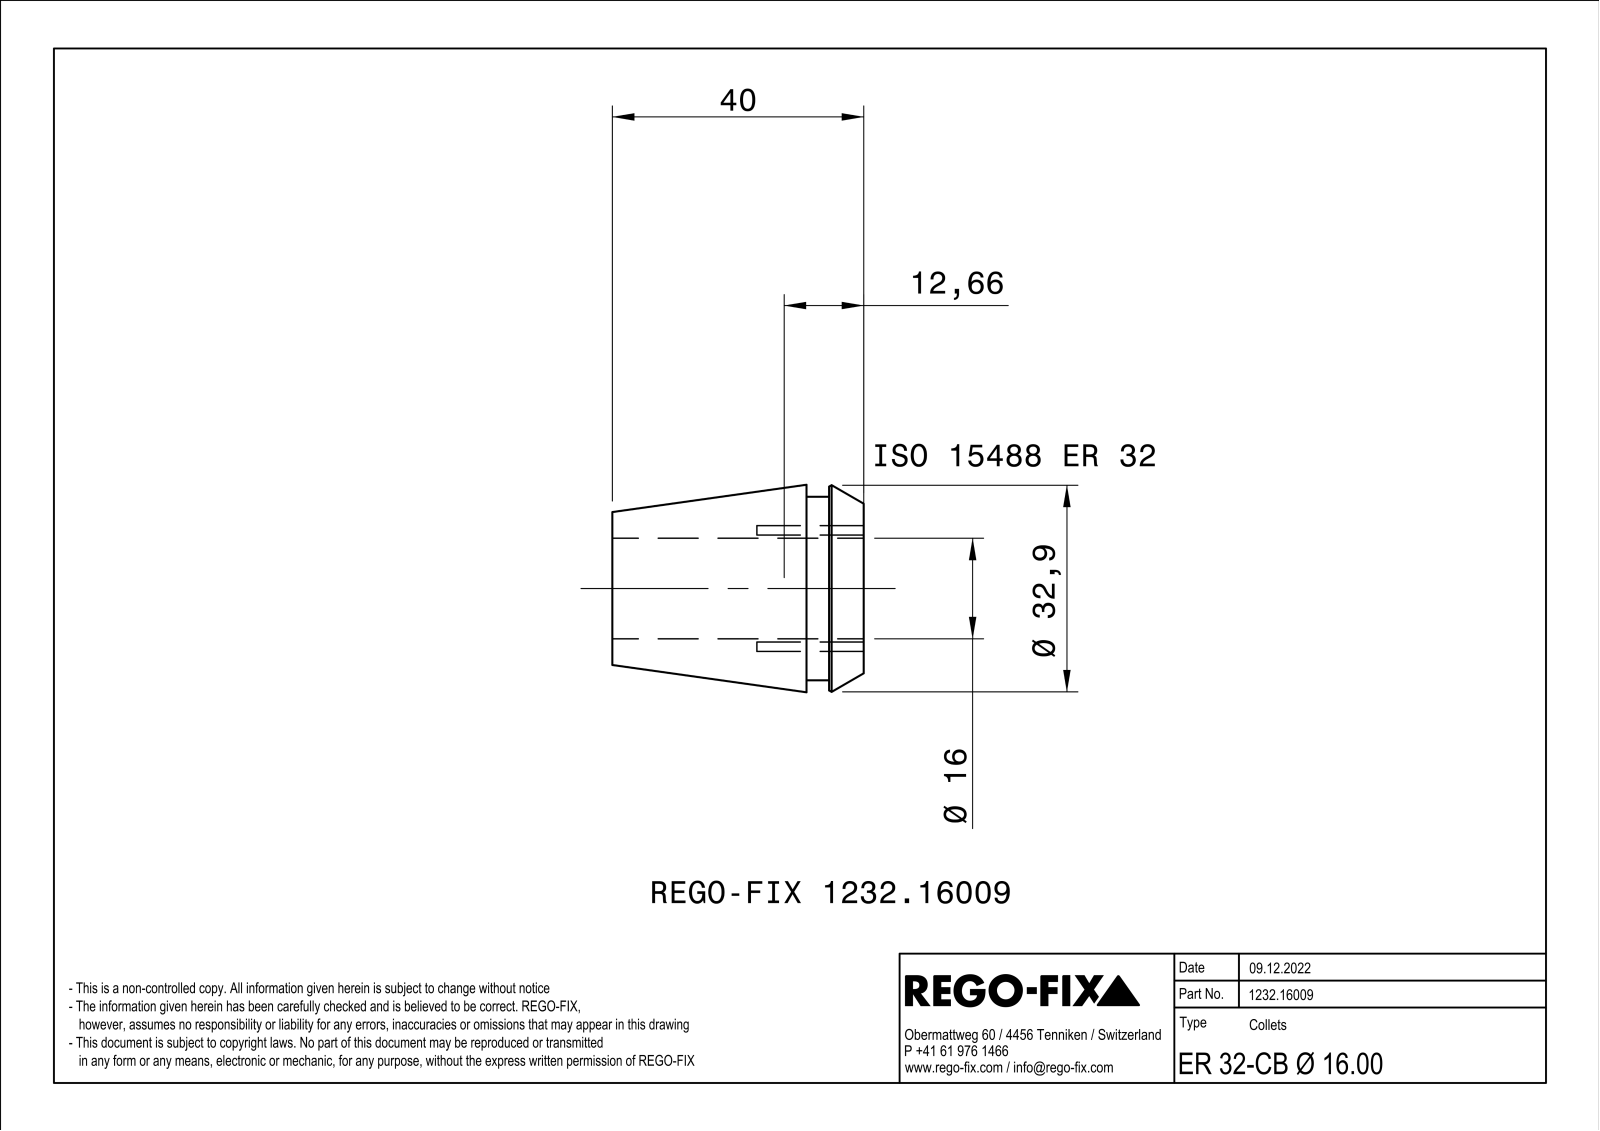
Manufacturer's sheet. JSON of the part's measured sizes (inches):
{"part_name": "NOCUT", "step_written_by": "SIEMENS PLM Software Solid Edge ST10 (AUTOMOTIVE_DESIGN)", "units": "inches", "bodies": {"solids": 1, "faces": 178, "planar": 64, "cylindrical": 21, "other": 93}, "overall_size": [1.575, 1.299, 1.299], "volume_in3": 0.966, "surface_area_in2": 19.02, "round_holes": [[0.059, 4], [0.63, 1]], "round_bosses_or_shafts": [[1.299, 1], [1.15, 1]], "face_to_face_distances": [0.031, 1.575, 0.217, 1.358, 0.358, 0.142, 1.217], "hole_center_spacings": [0.364, 0.515, 0.729]}
